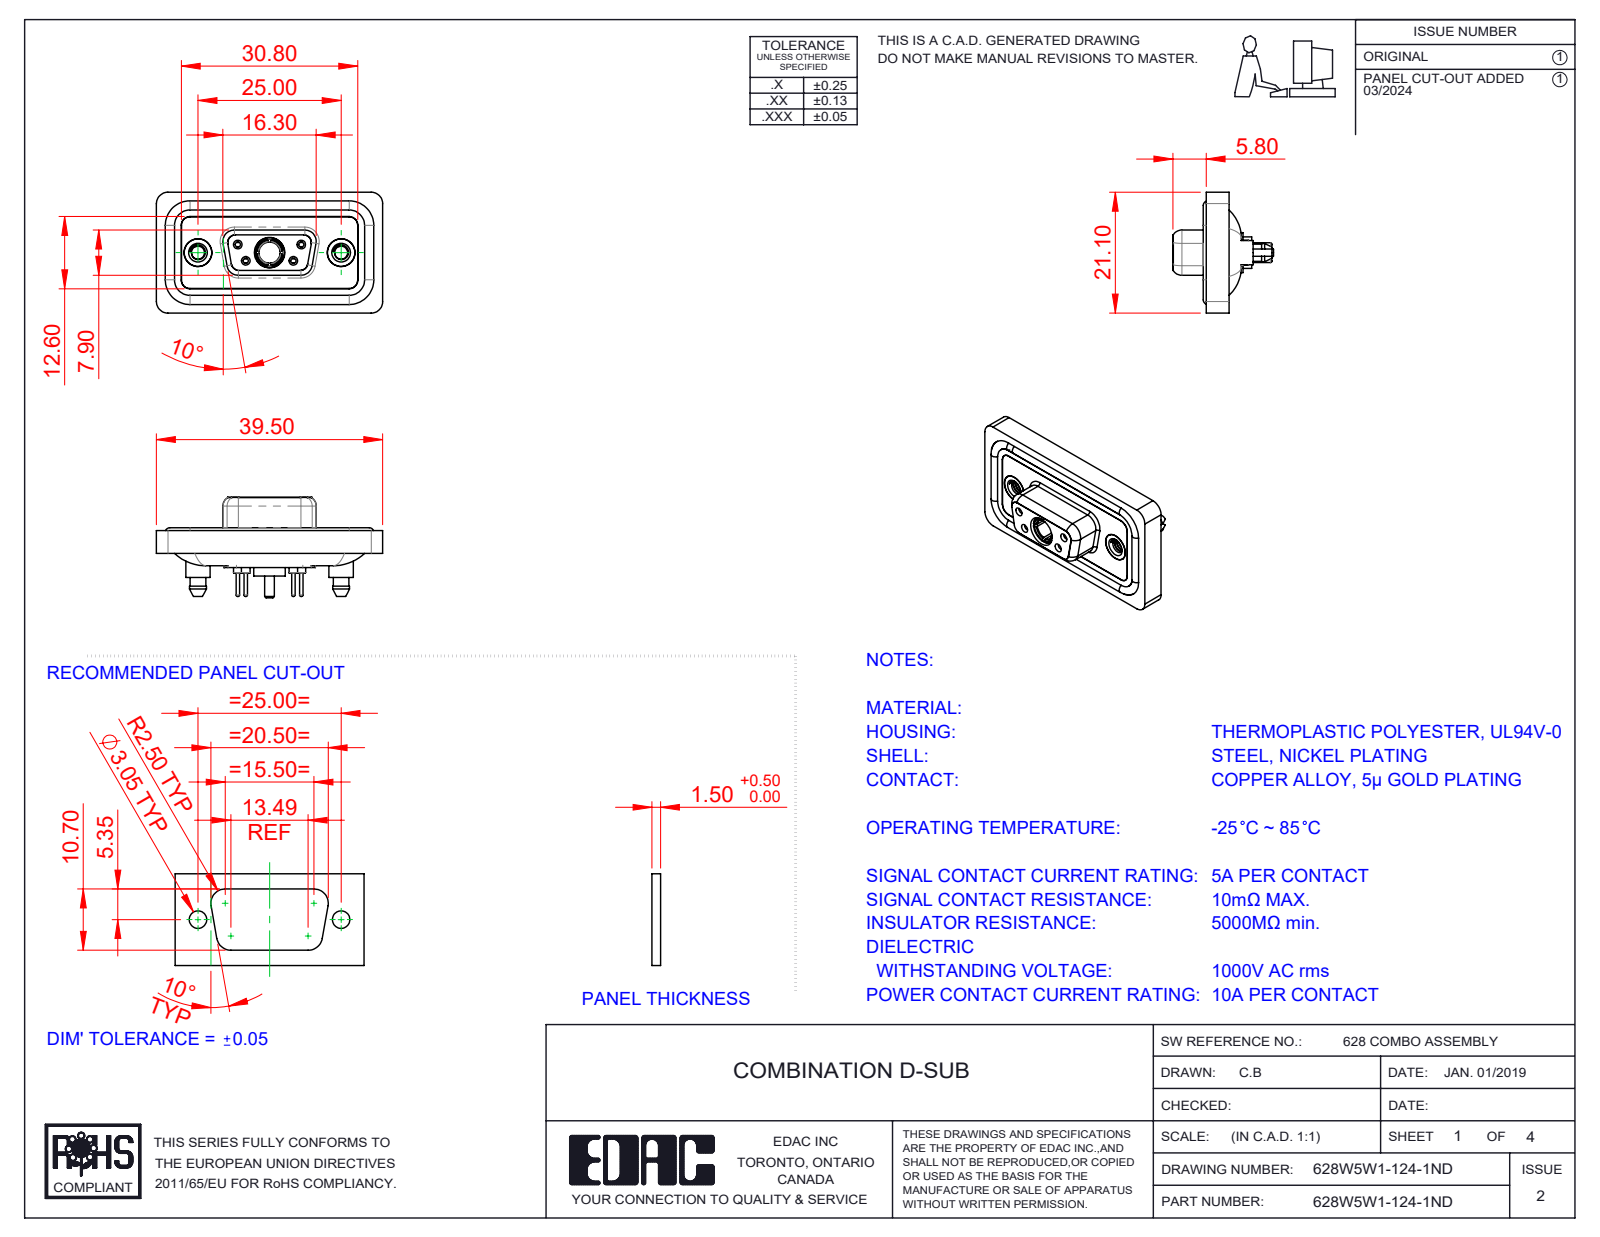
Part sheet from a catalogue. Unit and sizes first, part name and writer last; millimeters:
Units: millimetres
Overall size (bounding box): 39.5 × 21.1 × 17.55
Round holes (diameter × count): ⌀0.9 ×4, ⌀1.1 ×4, ⌀1.5 ×4, ⌀2 ×4, ⌀4.85 ×3, ⌀1.6 ×2, ⌀1.7 ×2, ⌀2.26 ×2, ⌀4 ×2, ⌀4.05 ×2, ⌀5 ×2, ⌀3.7 ×1
Round bosses / shafts (diameter × count): ⌀1.6 ×6, ⌀2.2 ×4, ⌀0.6 ×4, ⌀5.4 ×2, ⌀4.95 ×2, ⌀4.8 ×2, ⌀4.25 ×2, ⌀5.5 ×1
Partial cylindrical surfaces — rounded edges, fillets, slot ends (radius × count): R1.5 ×24, R2 ×18, R1.6 ×10, R1.35 ×8, R0.25 ×4, R0.5 ×4, R0.6 ×4, R0.65 ×4
Main face-to-face distances: 0.4, 2.9, 1.8, 1.1, 1.6, 0.5, 5.65, 7.45, 5.35, 3.6
Hole centre spacings: 3.16, 5.72, 7.1, 12.5, 18.1, 4.39, 4.4, 8.31
Volume: 4 888 mm³ · Surface area: 7 962 mm²
Bodies: 13 solids, 746 faces (210 planar, 335 cylindrical, 201 other)
Part name (STEP PRODUCT): 628Combo Threaded Boardlock_D; 628Combo Shell Rear_09 Contacts; 628Combo Shell Front_09 Contacts; 628Combo Housing_5W1 (+5 more)
STEP written by: SolidWorks 2023 (CONFIG_CONTROL_DESIGN)
